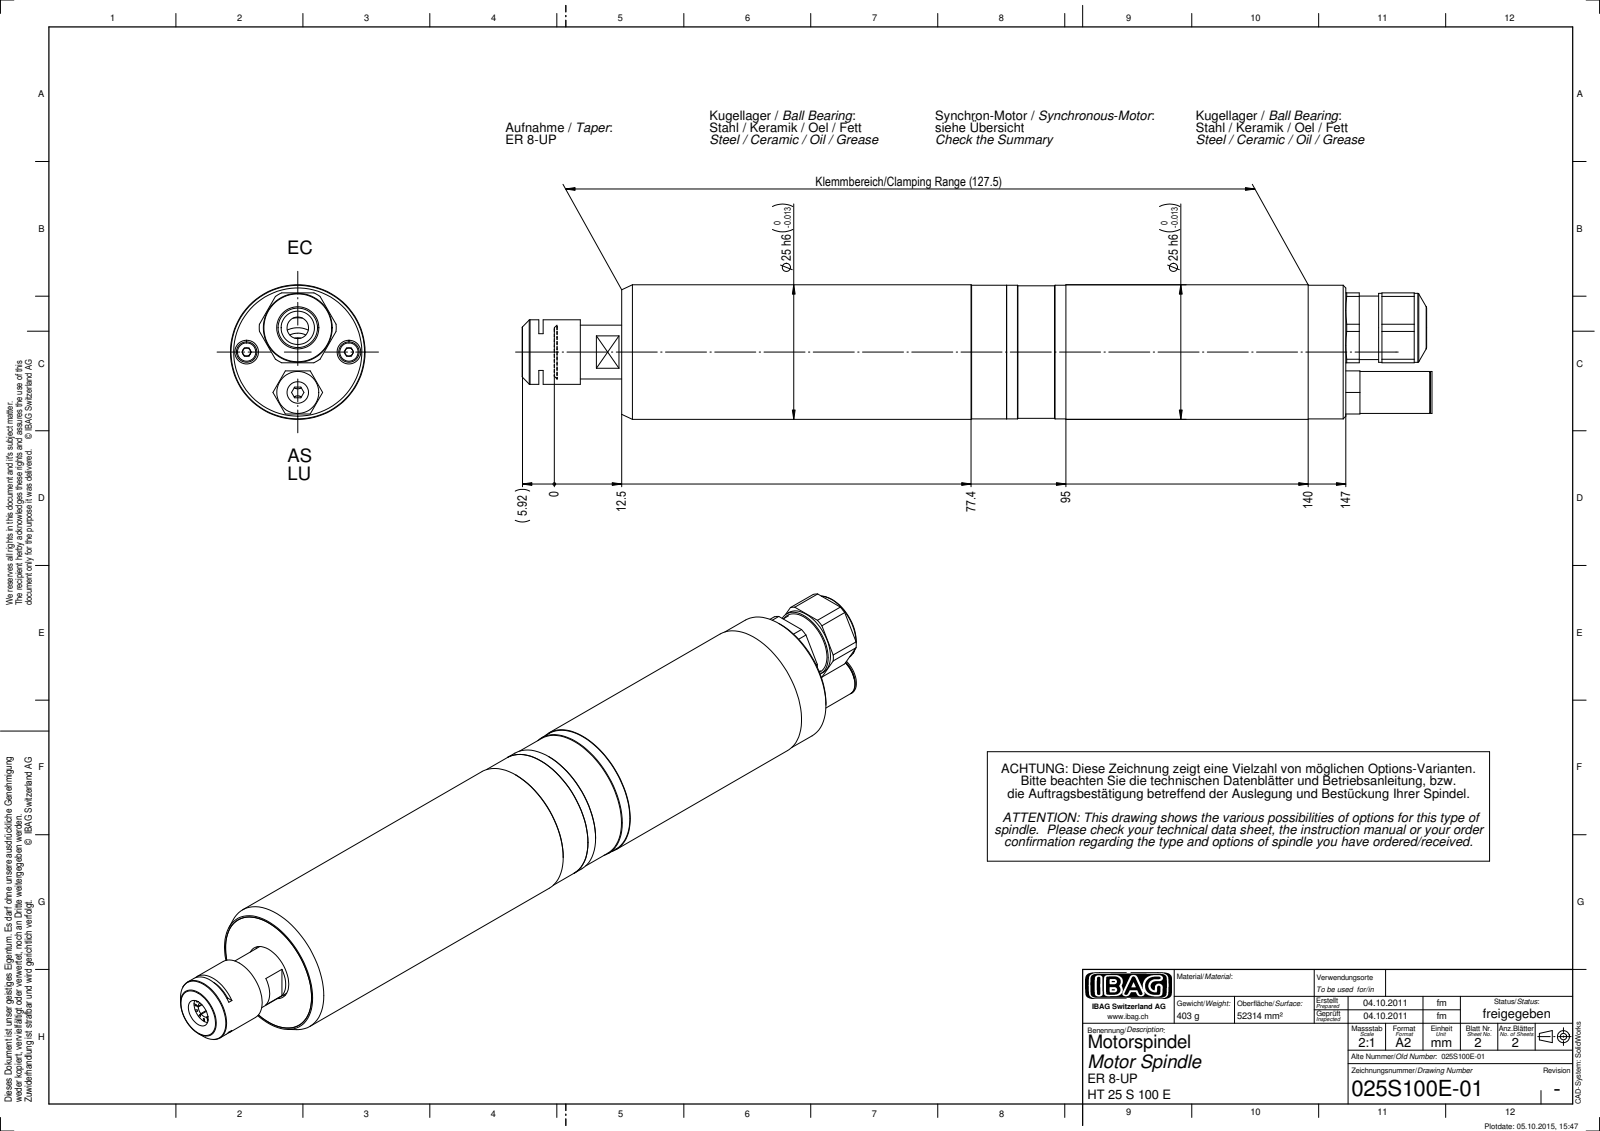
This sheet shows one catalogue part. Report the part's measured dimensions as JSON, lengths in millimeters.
{"part_name": "025S100E-01", "step_written_by": "SolidWorks 2010 (CONFIG_CONTROL_DESIGN)", "units": "millimeters", "bodies": {"solids": 0, "faces": 192, "planar": 83, "cylindrical": 65, "other": 44}, "overall_size": [167.64, 25, 25], "round_holes": [[4, 2], [4.4, 2], [3, 1], [6.2, 1], [10.6, 1]], "round_bosses_or_shafts": [[3.8, 2], [25, 1], [24.8, 1], [24.6, 1], [22.6, 1], [12.8, 1], [12, 1], [11.79, 1]], "partial_cylinders_radius": [[2.1, 1], [7.15, 1]], "face_to_face_distances": [134.5, 1.8, 132.7, 69.7, 71.5, 63, 13, 1.5, 17.14, 18.94], "hole_center_spacings": [9.5, 10.51, 12.1, 4.5, 7.5, 12, 19]}
